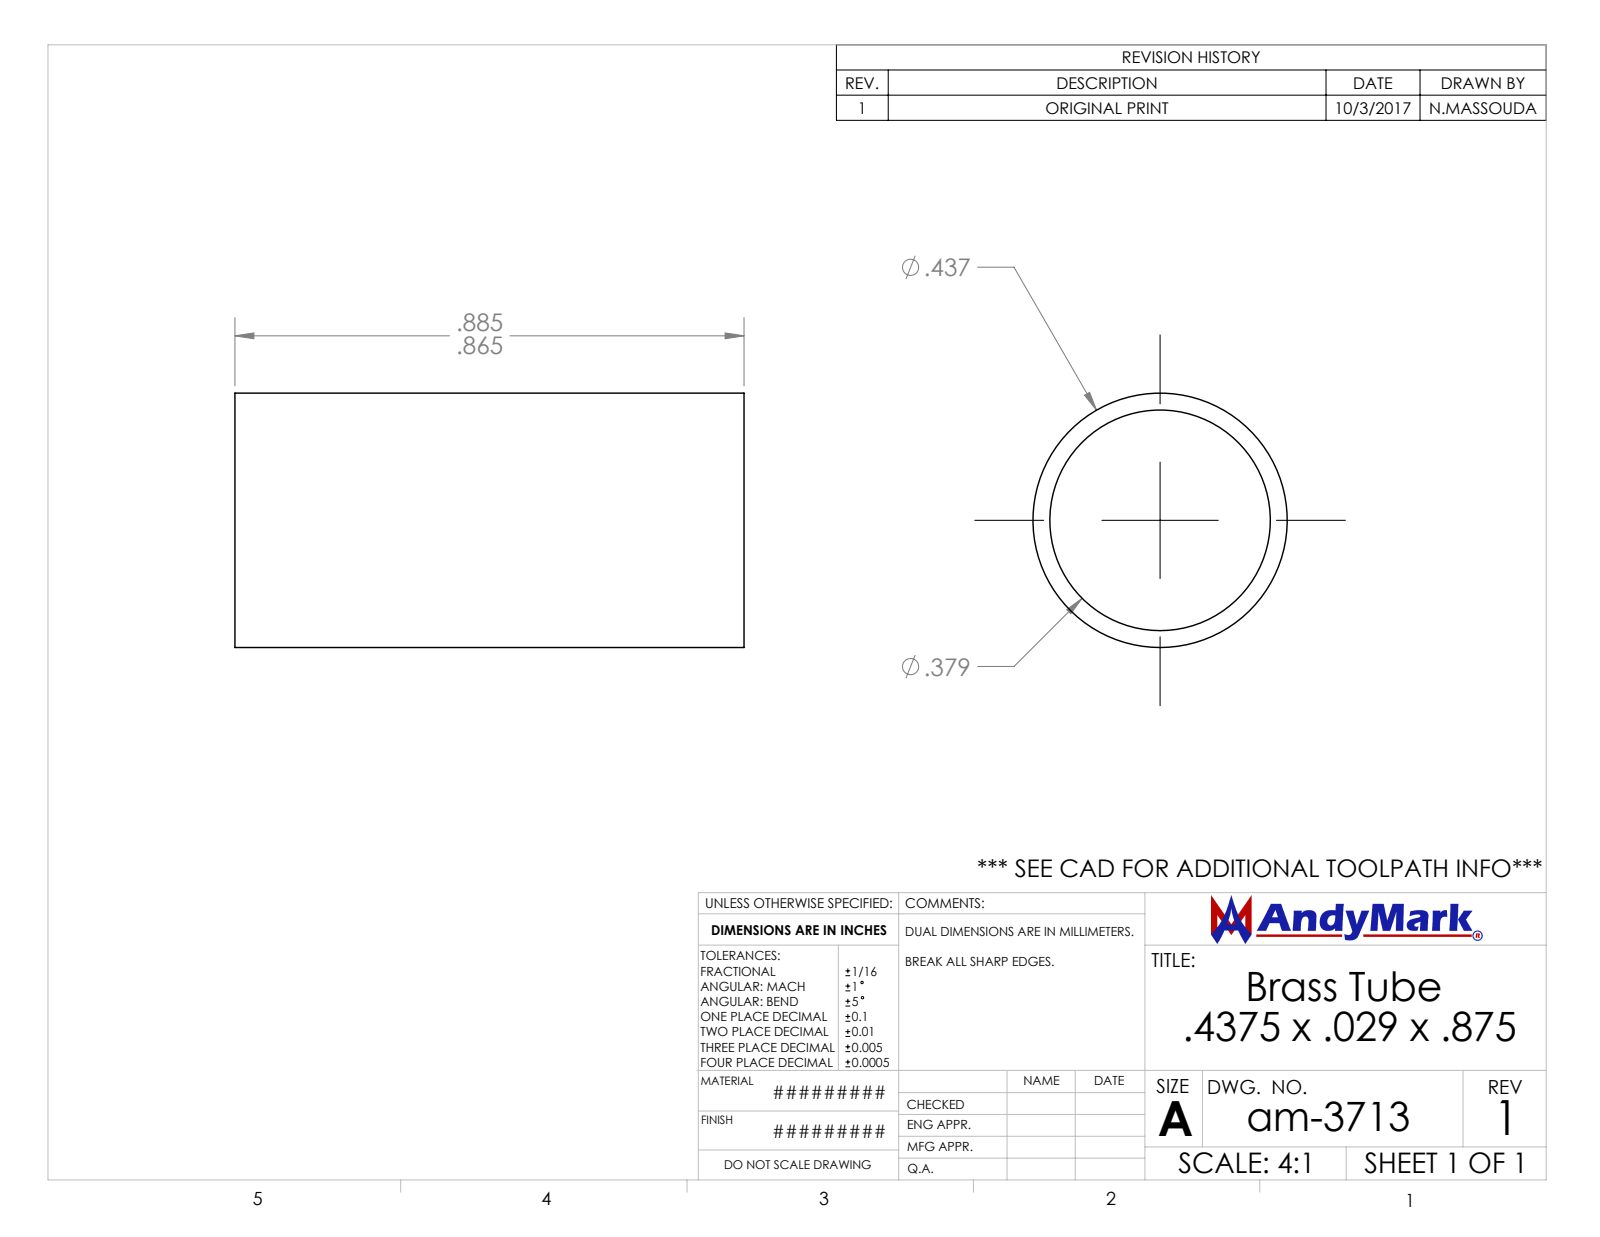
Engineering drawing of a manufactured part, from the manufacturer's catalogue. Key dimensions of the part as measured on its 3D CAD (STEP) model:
Part name (STEP PRODUCT): am-3713 Brass Tube .4375 x .029 x .875
STEP written by: SolidWorks 2021 (AUTOMOTIVE_DESIGN)
Units: inches
Bodies: 1 solid, 6 faces (2 planar, 4 cylindrical, 0 other)
Overall size (bounding box): 0.875 × 0.437 × 0.437
Volume: 0.033 in³ · Surface area: 2.32 in²
Round holes (diameter × count): ⌀0.379 ×1
Round bosses / shafts (diameter × count): ⌀0.437 ×1
Main face-to-face distances: 0.875
